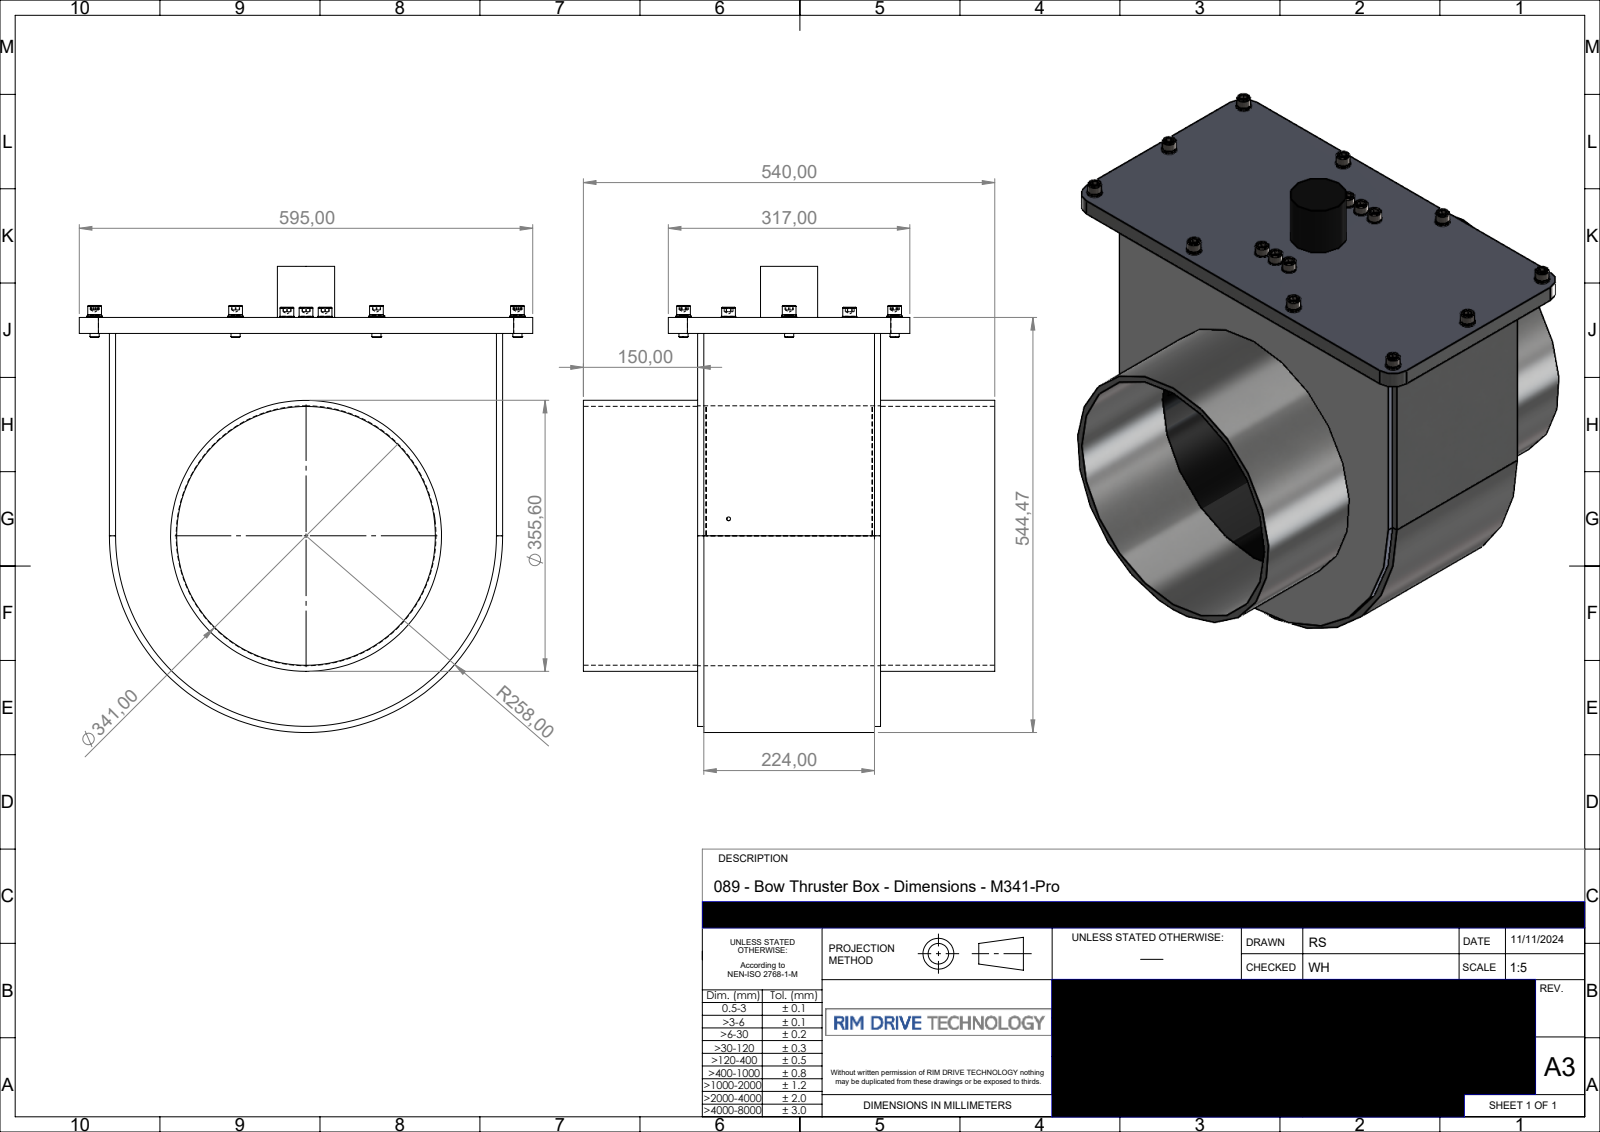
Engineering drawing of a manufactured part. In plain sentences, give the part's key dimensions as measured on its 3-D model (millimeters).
The part is named "P-089-030-rev-A-M341-Pro". Its 3-D file was written by "SolidWorks 2024 (AUTOMOTIVE_DESIGN)". It is 11 solids with 505 faces: 315 planar, 102 cylindrical and 88 other. Overall it measures 611.47 by 595 by 540 millimeters. Its volume is 42 810 000 cubic millimeters and its surface area 1 870 000 square millimeters. Round holes: 10 of diameter 10.2, 6 of diameter 12.7, 2 of diameter 5, 1 of diameter 339.6, 1 of diameter 341. Round bosses or shafts: 16 of diameter 18, 16 of diameter 12, 10 of diameter 20, 10 of diameter 18.1, 6 of diameter 19, 1 of diameter 355.6, 1 of diameter 75. Partial cylindrical surfaces (rounded edges, fillets, slot ends): 4 of radius 25, 1 of radius 170.5, 1 of radius 250, 1 of radius 258. The main face-to-face distances are 240, 21, 516, 8, 38.5, 278.5, 46.5, 270.5, 232, 111.5. The hole center spacings are 185, 333.1, 25, 89.65, 109.71, 131.48, 138.5, 160.95.
